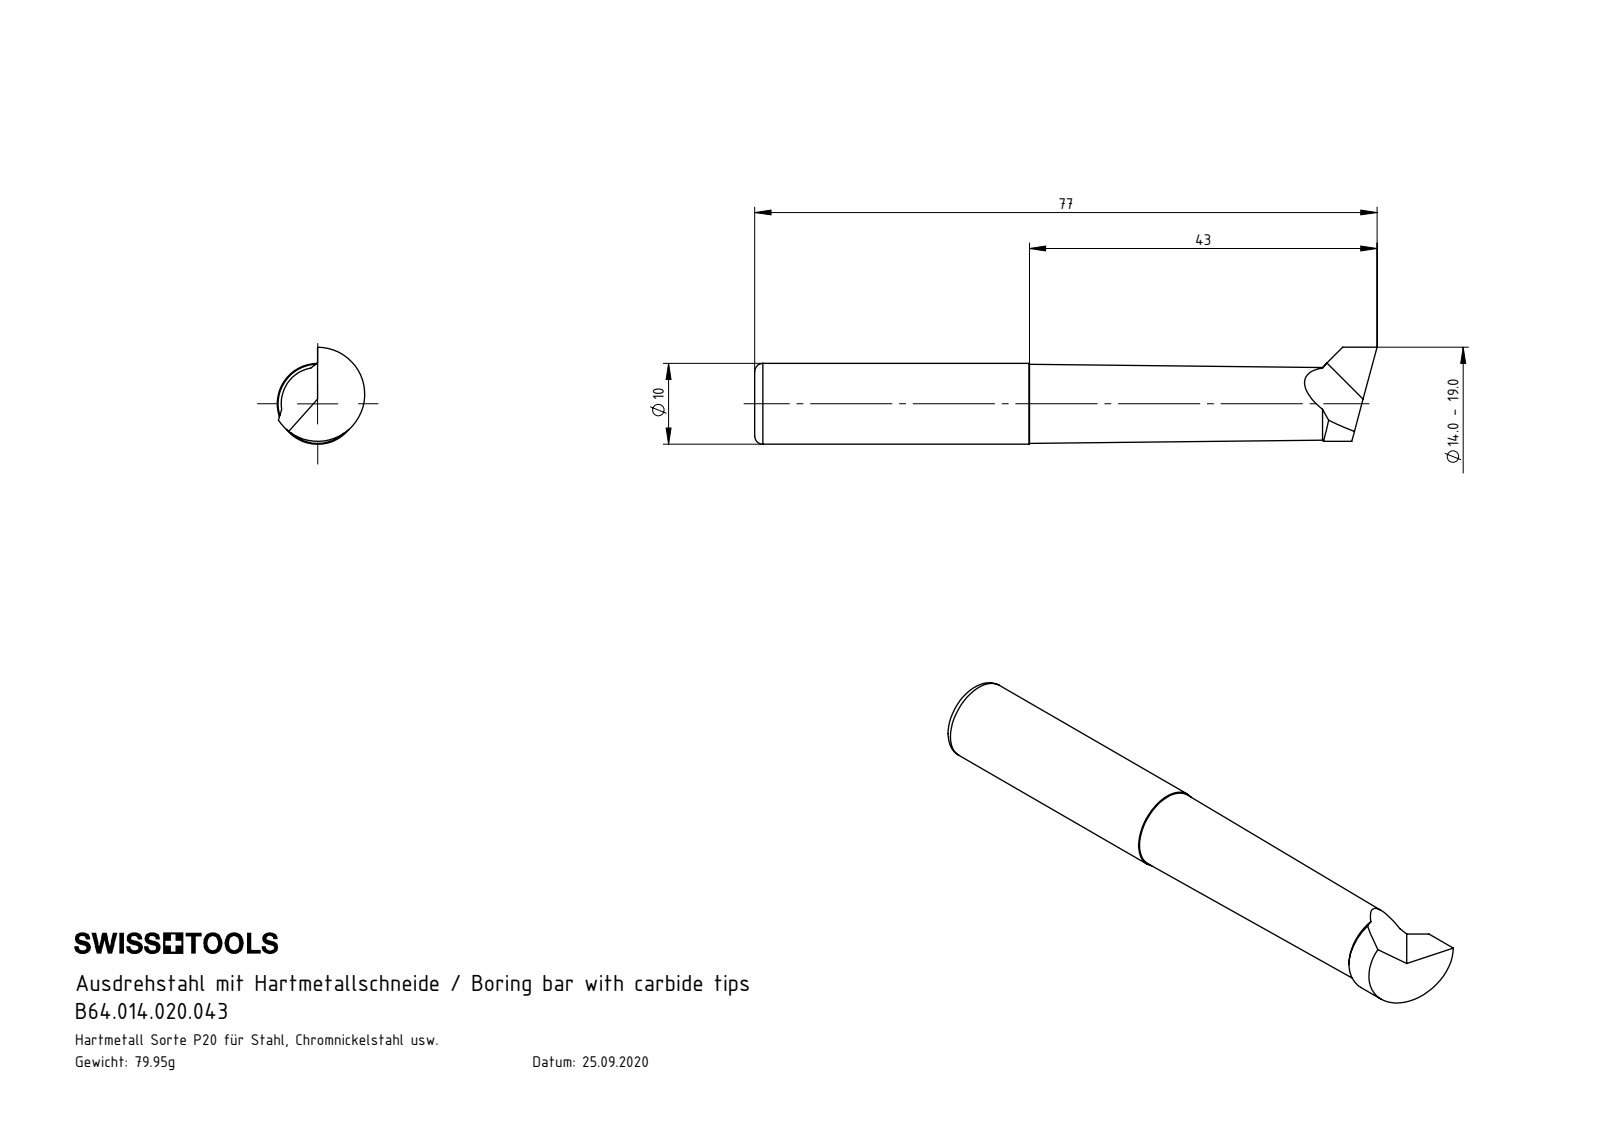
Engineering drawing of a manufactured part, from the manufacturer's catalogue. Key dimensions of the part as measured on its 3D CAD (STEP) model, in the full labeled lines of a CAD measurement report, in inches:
Part name (STEP PRODUCT): B64.014.020.043
STEP written by: SolidWorks 2022 (CONFIG_CONTROL_DESIGN)
Units: inches
Bodies: 1 solid, 16 faces (4 planar, 3 cylindrical, 9 other)
Overall size (bounding box): 3.031 × 0.472 × 0.426
Volume: 0.336 in³ · Surface area: 3.801 in²
Round bosses / shafts (diameter × count): ⌀0.394 ×1
Partial cylindrical surfaces — rounded edges, fillets, slot ends (radius × count): R0.229 ×1
